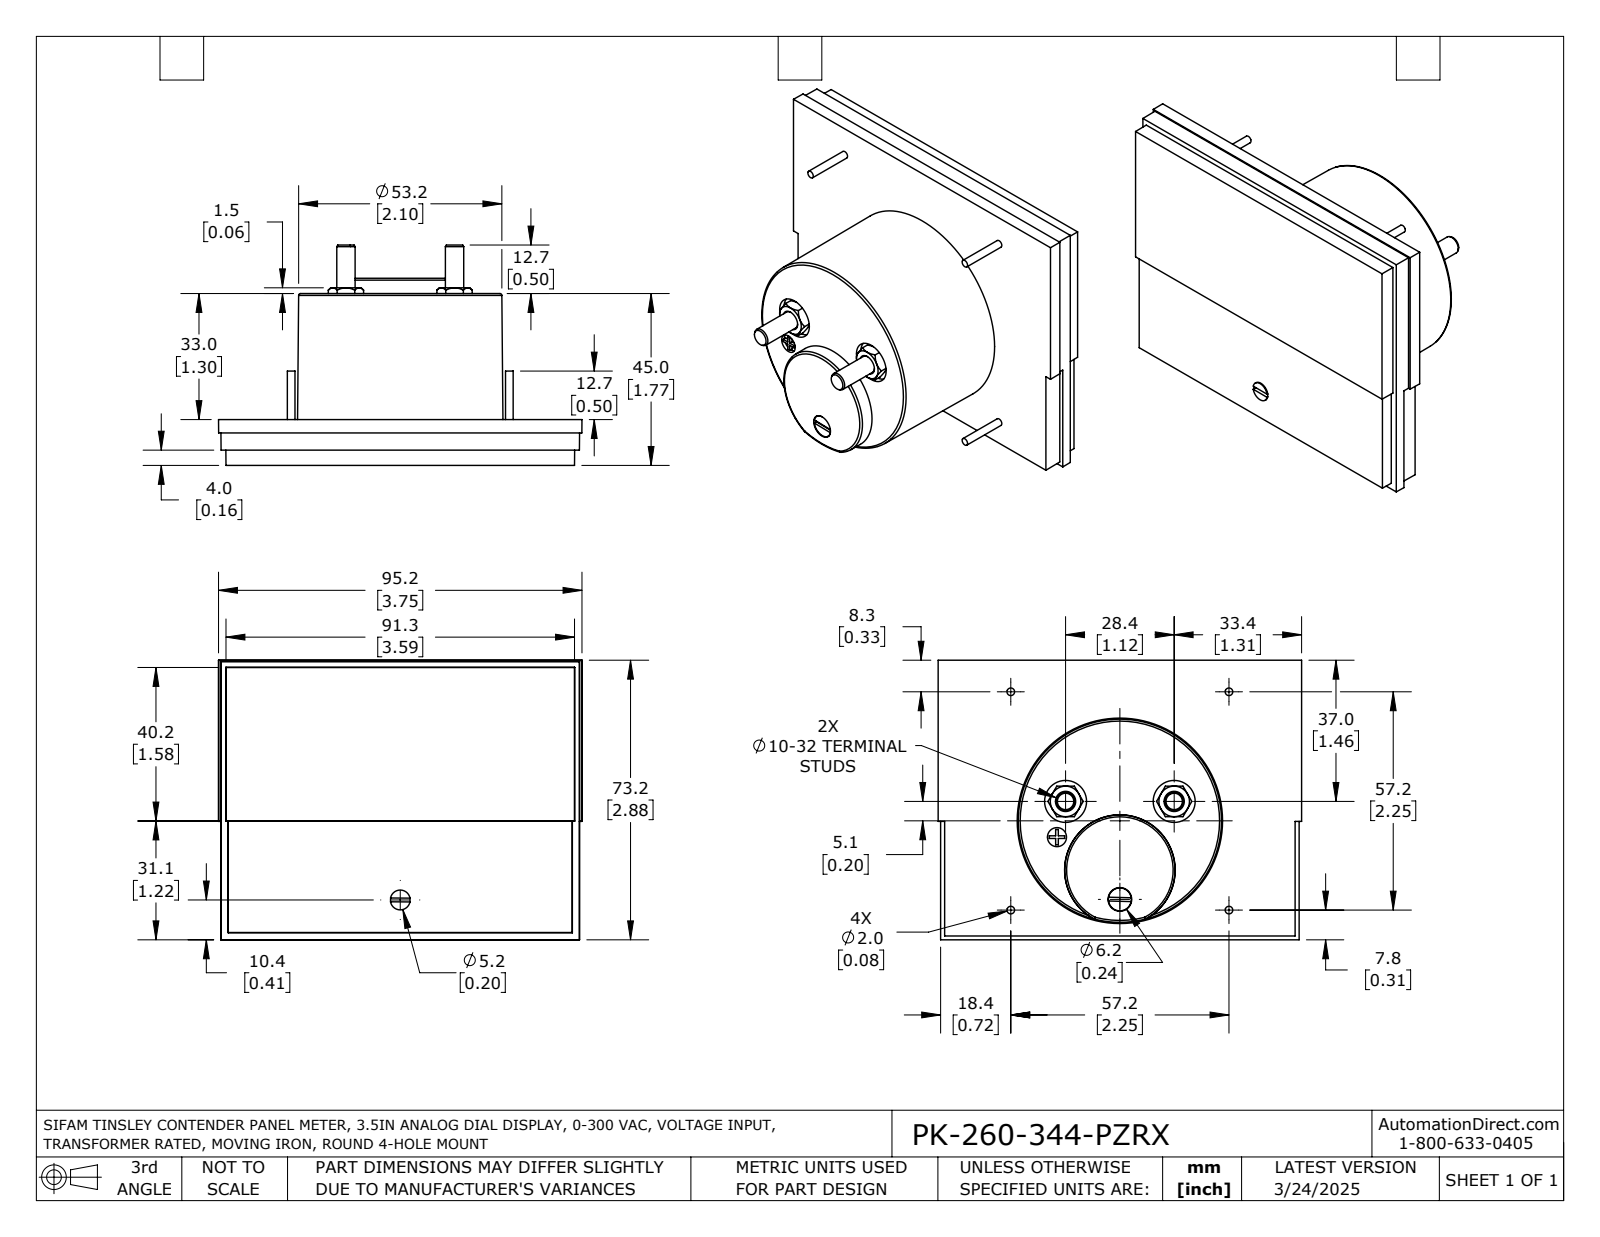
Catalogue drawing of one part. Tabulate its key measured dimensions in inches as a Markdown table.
| quantity | value |
| --- | --- |
| part name | PK-260-344-PZRX |
| STEP written by | SolidWorks 2021 (AUTOMOTIVE_DESIGN) |
| units | inches |
| bodies | 1 solid, 163 faces (76 planar, 31 cylindrical, 56 other) |
| overall size | 3.748 × 2.882 × 2.272 |
| volume | 9.446 in³ |
| surface area | 38.39 in² |
| round holes (diameter × count) | 0.433 × 2, 0.197 × 1, 0.244 × 1 |
| round bosses / shafts (diameter × count) | 0.079 × 4, 0.189 × 2, 0.236 × 1, 0.205 × 1 |
| partial cylindrical surfaces (radius × count) | 0.1 × 1 |
| main face-to-face distances | 0.472, 0.03, 0.443, 1.772, 1.299, 1.742, 0.157, 0.073, 0.315, 1.457 |
| hole center spacings | 1.155, 0.379, 0.912, 1.12, 1.263 |
